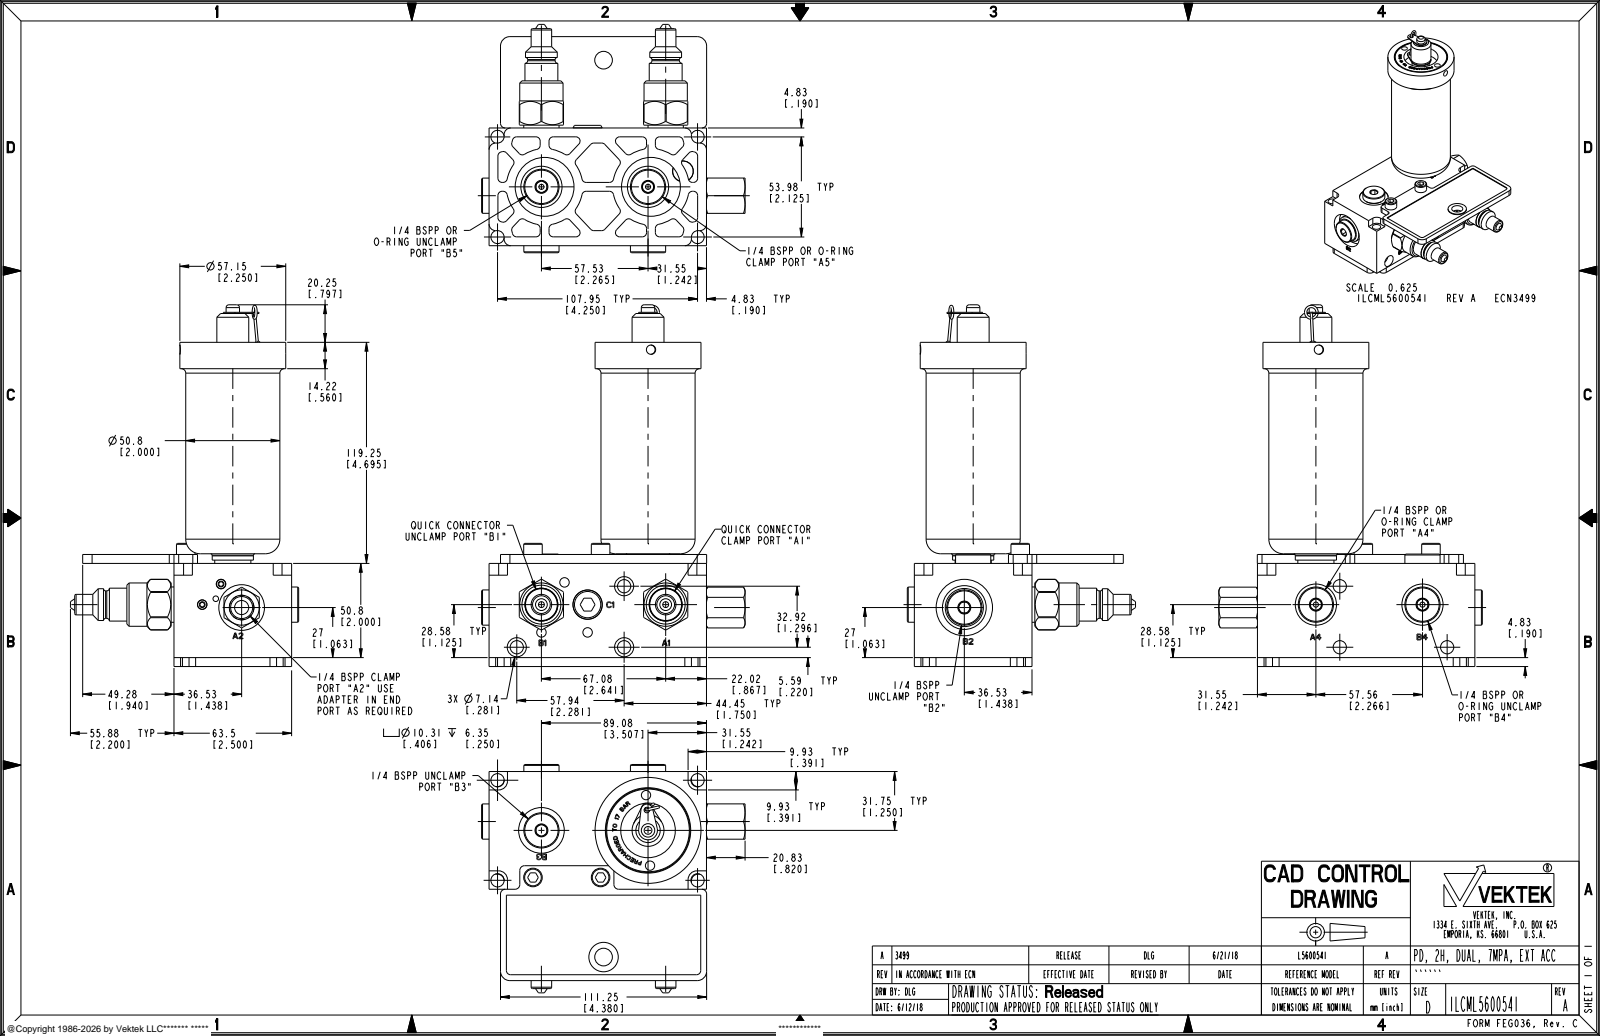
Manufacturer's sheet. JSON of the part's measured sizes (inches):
{"part_name": "ILCML5600541; 30871966; 45600511", "step_written_by": "PRO/ENGINEER BY PARAMETRIC TECHNOLOGY CORPORATION, 2013320 (CONFIG_CONTROL_DESIGN)", "units": "inches", "bodies": {"solids": 5, "faces": 1885, "planar": 1326, "cylindrical": 307, "other": 252}, "overall_size": [7.682, 5.599, 4.85], "volume_in3": 41.6, "surface_area_in2": 176.4, "round_holes": [[0.281, 8], [0.875, 4], [0.197, 3], [0.201, 3], [0.406, 3], [0.97, 3], [0.079, 2], [0.118, 2], [0.123, 2], [0.202, 2], [1.25, 2], [0.118, 1]], "round_bosses_or_shafts": [[0.748, 5], [0.92, 2], [0.75, 2], [0.699, 2], [0.675, 2], [0.585, 2], [0.436, 2], [0.394, 2]], "partial_cylinders_radius": [[0.09, 70], [0.14, 12], [0.1, 6], [0.187, 4], [0.2, 3], [0.536, 2], [0.812, 2], [0.108, 1]], "face_to_face_distances": [2, 2.5, 2.19, 0.19, 0.17, 2.17, 2.36, 4.62, 2.38, 0.02], "hole_center_spacings": [0.75, 2.125, 2.198, 2.26, 2.265, 2.281, 4.25, 4.752]}
